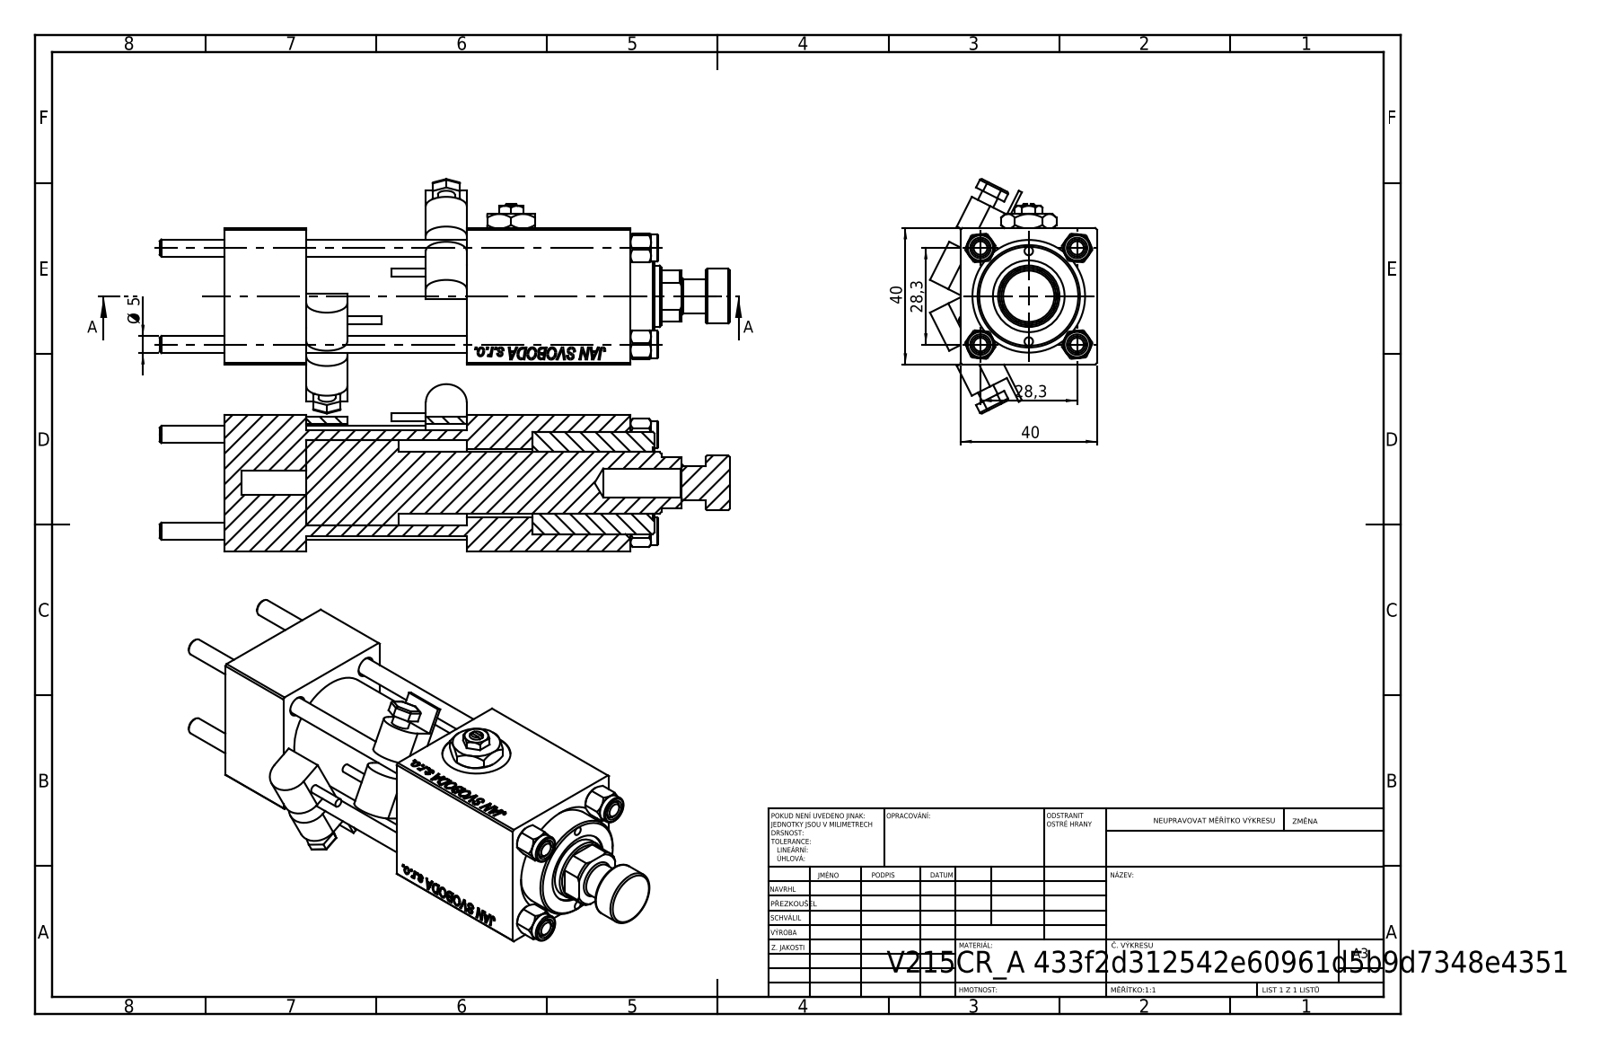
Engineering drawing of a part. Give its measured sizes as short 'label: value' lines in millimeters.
name: V215CR_VCP; MSRF_MSRG1; V215CR_BODY_A; NUT_M5 (+4 more)
written by: SolidWorks 2019 (CONFIG_CONTROL_DESIGN)
unit: mm
bodies: 14 solids, 1259 faces (581 planar, 116 cylindrical, 562 other)
size: 167 × 68.71 × 48.93
volume: 70 898 mm³; area: 66 962 mm²
holes: 4× ⌀5, 3× ⌀20, 2× ⌀2.5, 2× ⌀7, 2× ⌀13.16, 1× ⌀8.5, 1× ⌀18, 1× ⌀21, 1× ⌀25, 1× ⌀30
bosses: 4× ⌀8, 2× ⌀5, 2× ⌀2.5, 1× ⌀31, 1× ⌀16, 1× ⌀10
rounds: 12× R0.5, 4× R6, 1× R8.5
face distances: 40, 24, 71, 47, 90.3, 66.3, 19.3, 8, 119, 95
hole spacings: 14.18, 20.01, 28.3, 30.84, 13.25, 40.02, 26.5, 72
